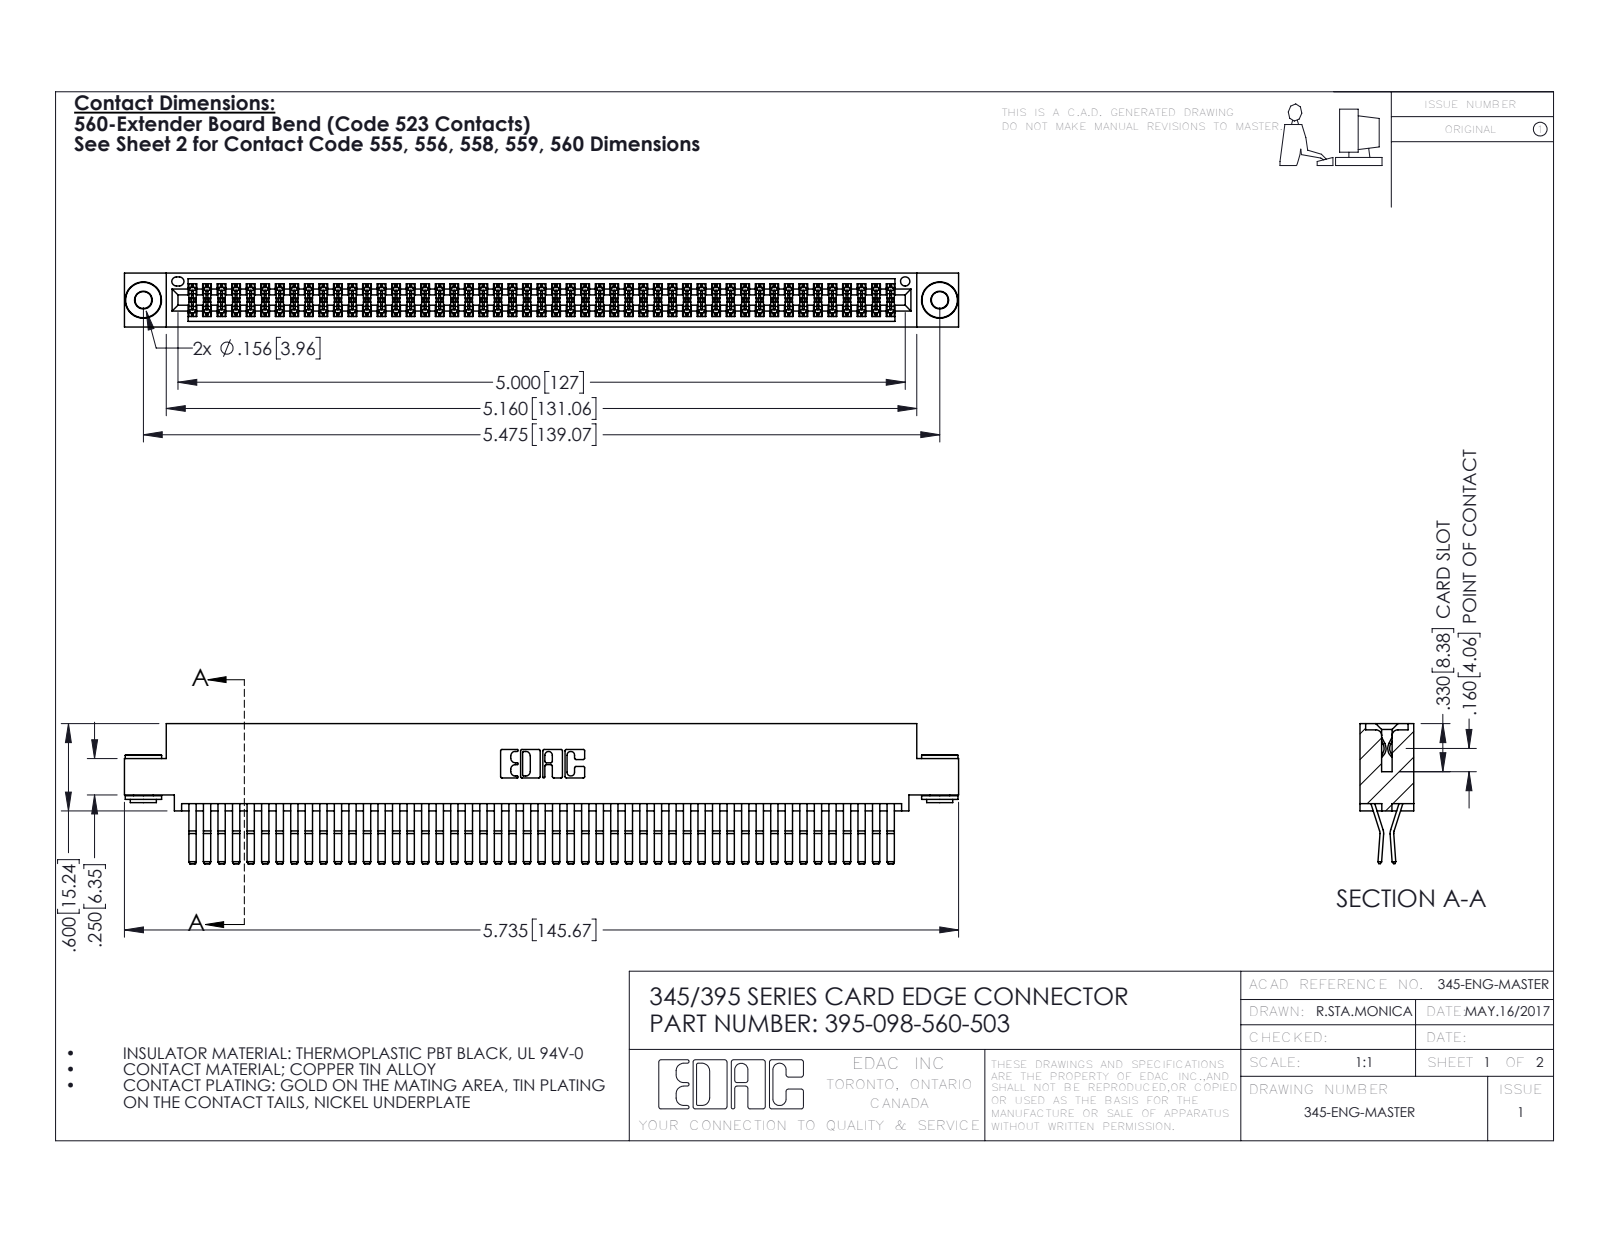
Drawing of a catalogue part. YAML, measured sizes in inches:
part_name: "395-098-560-503; 345 Part_0.110 Offset - 0.156 Dia-TH; 345-250-002_345-250-002-102; 345-292-001_560 Tail"
step_written_by: "SolidWorks 2016 (CONFIG_CONTROL_DESIGN)"
units: inches
bodies: {solids: 101, faces: 5264, planar: 3328, cylindrical: 1928, other: 8}
overall_size: [5.735, 0.962, 0.37]
volume: 0.903
surface_area: 37.15
round_holes:
  - {diameter: 0.116, count: 2}
  - {diameter: 0.156, count: 2}
  - {diameter: 0.064, count: 1}
round_bosses_or_shafts:
  - {diameter: 0.25, count: 2}
  - {diameter: 0.18, count: 2}
  - {diameter: 0.136, count: 2}
partial_cylinders:
  - {radius: 0.006, count: 147}
  - {radius: 0.01, count: 22}
  - {radius: 0.007, count: 6}
  - {radius: 0.031, count: 6}
  - {radius: 0.026, count: 3}
  - {radius: 0.01, count: 2}
  - {radius: 0.014, count: 2}
  - {radius: 0.019, count: 2}
face_to_face_distances: [0.025, 0.072, 0.298, 0.37, 0.2, 0.098, 0.272, 0.225, 0.175, 0.149]
hole_center_spacings: [0.27, 5.239, 5.475]
